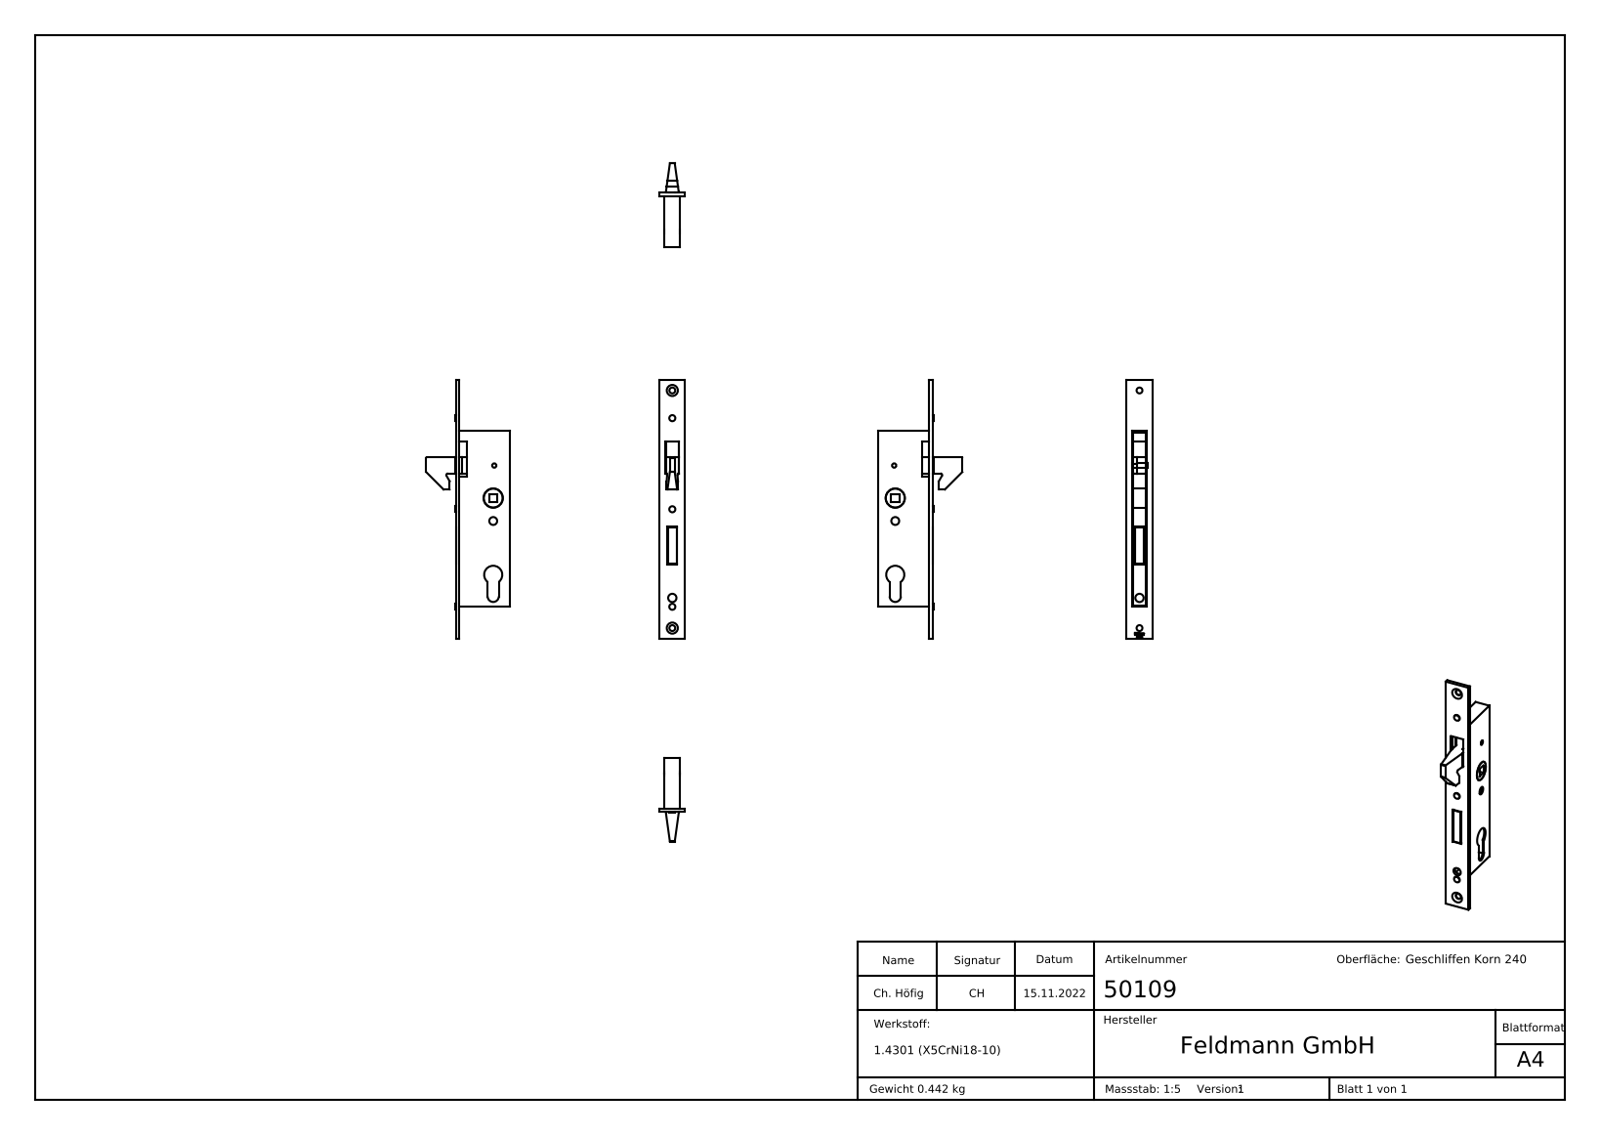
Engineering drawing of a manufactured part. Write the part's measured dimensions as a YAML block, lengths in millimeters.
part_name: "50109"
step_written_by: "SolidWorks 2018 (CONFIG_CONTROL_DESIGN)"
units: millimeters
bodies: {solids: 5, faces: 266, planar: 156, cylindrical: 25, other: 85}
overall_size: [243, 79, 24]
volume: 56463
surface_area: 51585
round_holes:
  - {diameter: 5.5, count: 2}
  - {diameter: 7.4, count: 1}
  - {diameter: 7.8, count: 1}
  - {diameter: 18, count: 1}
round_bosses_or_shafts:
  - {diameter: 5.7, count: 3}
  - {diameter: 17.8, count: 1}
  - {diameter: 4, count: 1}
  - {diameter: 3.8, count: 1}
partial_cylinders:
  - {radius: 0.5, count: 5}
  - {radius: 1.5, count: 1}
  - {radius: 5.25, count: 1}
  - {radius: 8.5, count: 1}
face_to_face_distances: [1.5, 13, 14.5, 11.5, 3, 4.75, 19.25, 6.25, 17.75, 8.1]
hole_center_spacings: [21.5, 28.3, 194.7, 223]
